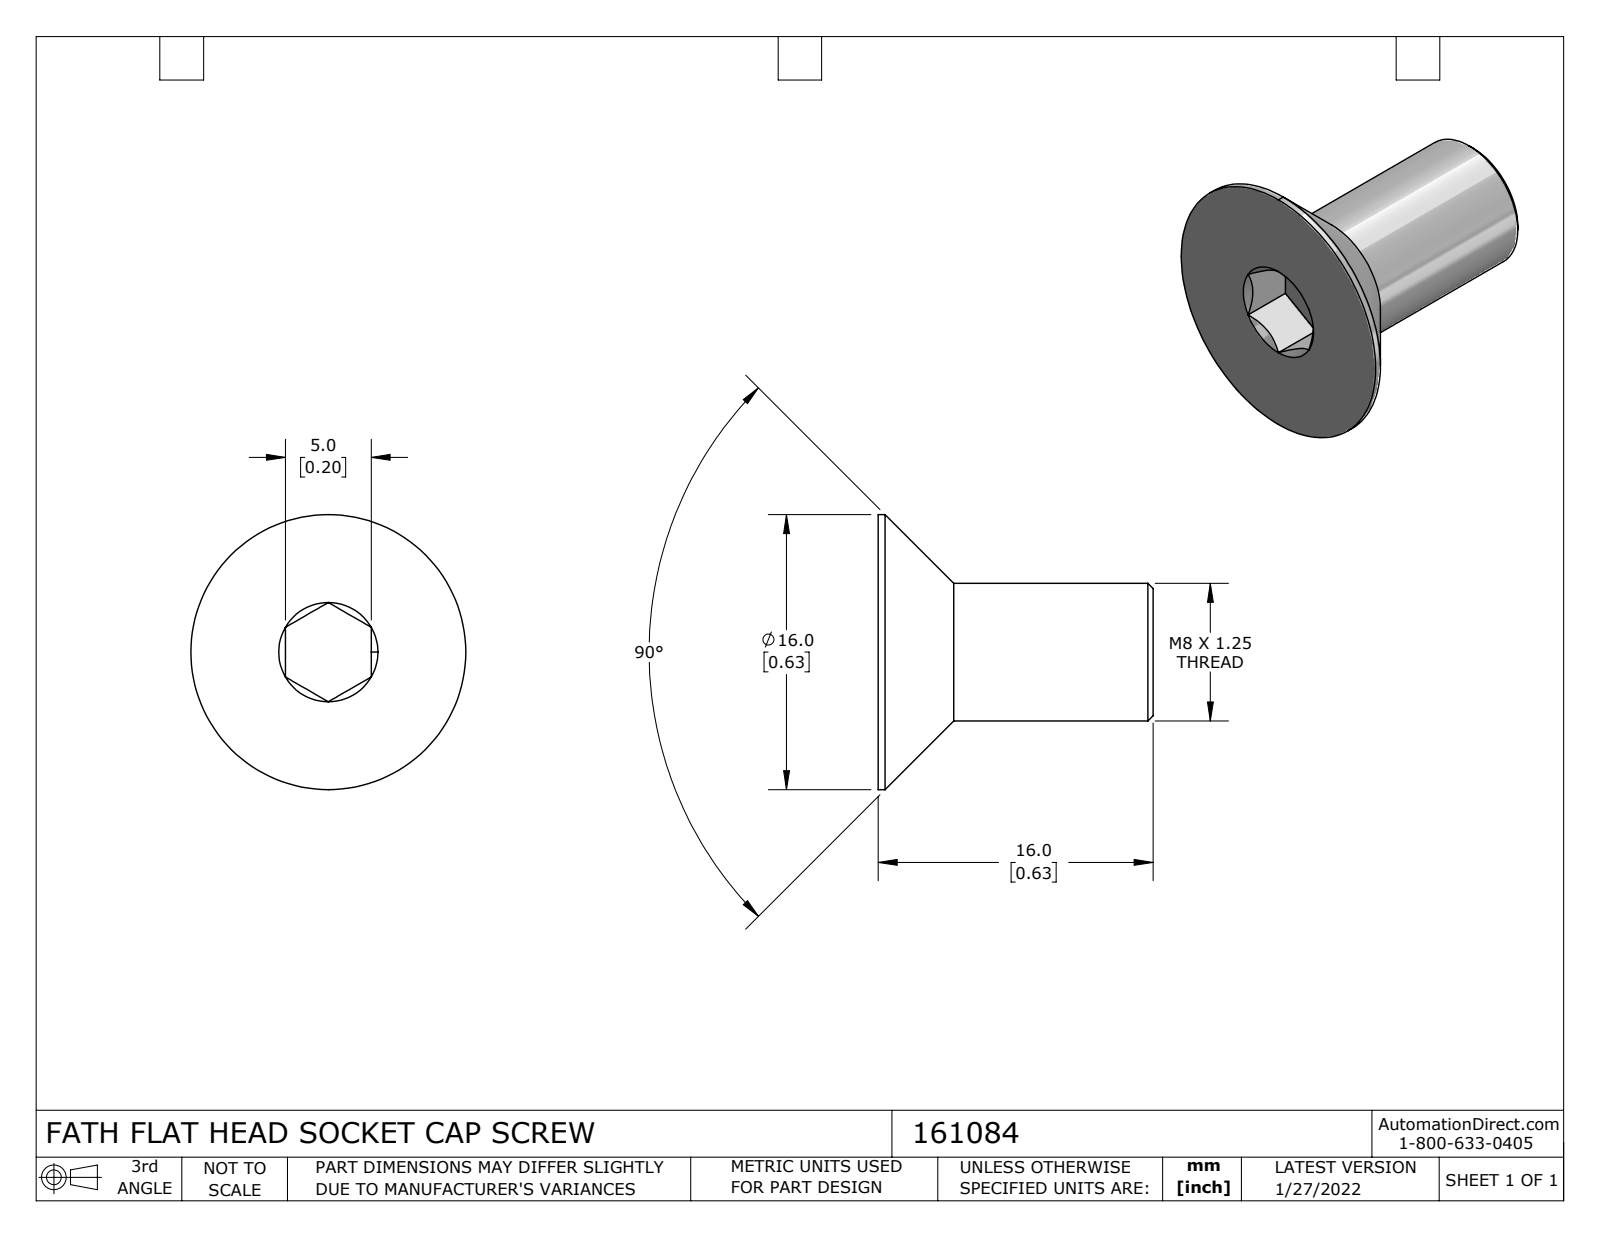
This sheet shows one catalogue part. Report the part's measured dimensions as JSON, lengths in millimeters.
{"part_name": "161084", "step_written_by": "SolidWorks 2021 (CONFIG_CONTROL_DESIGN)", "units": "millimeters", "bodies": {"solids": 1, "faces": 24, "planar": 9, "cylindrical": 4, "other": 11}, "overall_size": [16, 16, 16], "volume_mm3": 1064, "surface_area_mm2": 823, "round_bosses_or_shafts": [[16, 1], [8, 1]], "face_to_face_distances": [16, 5, 12.92, 3.08]}
